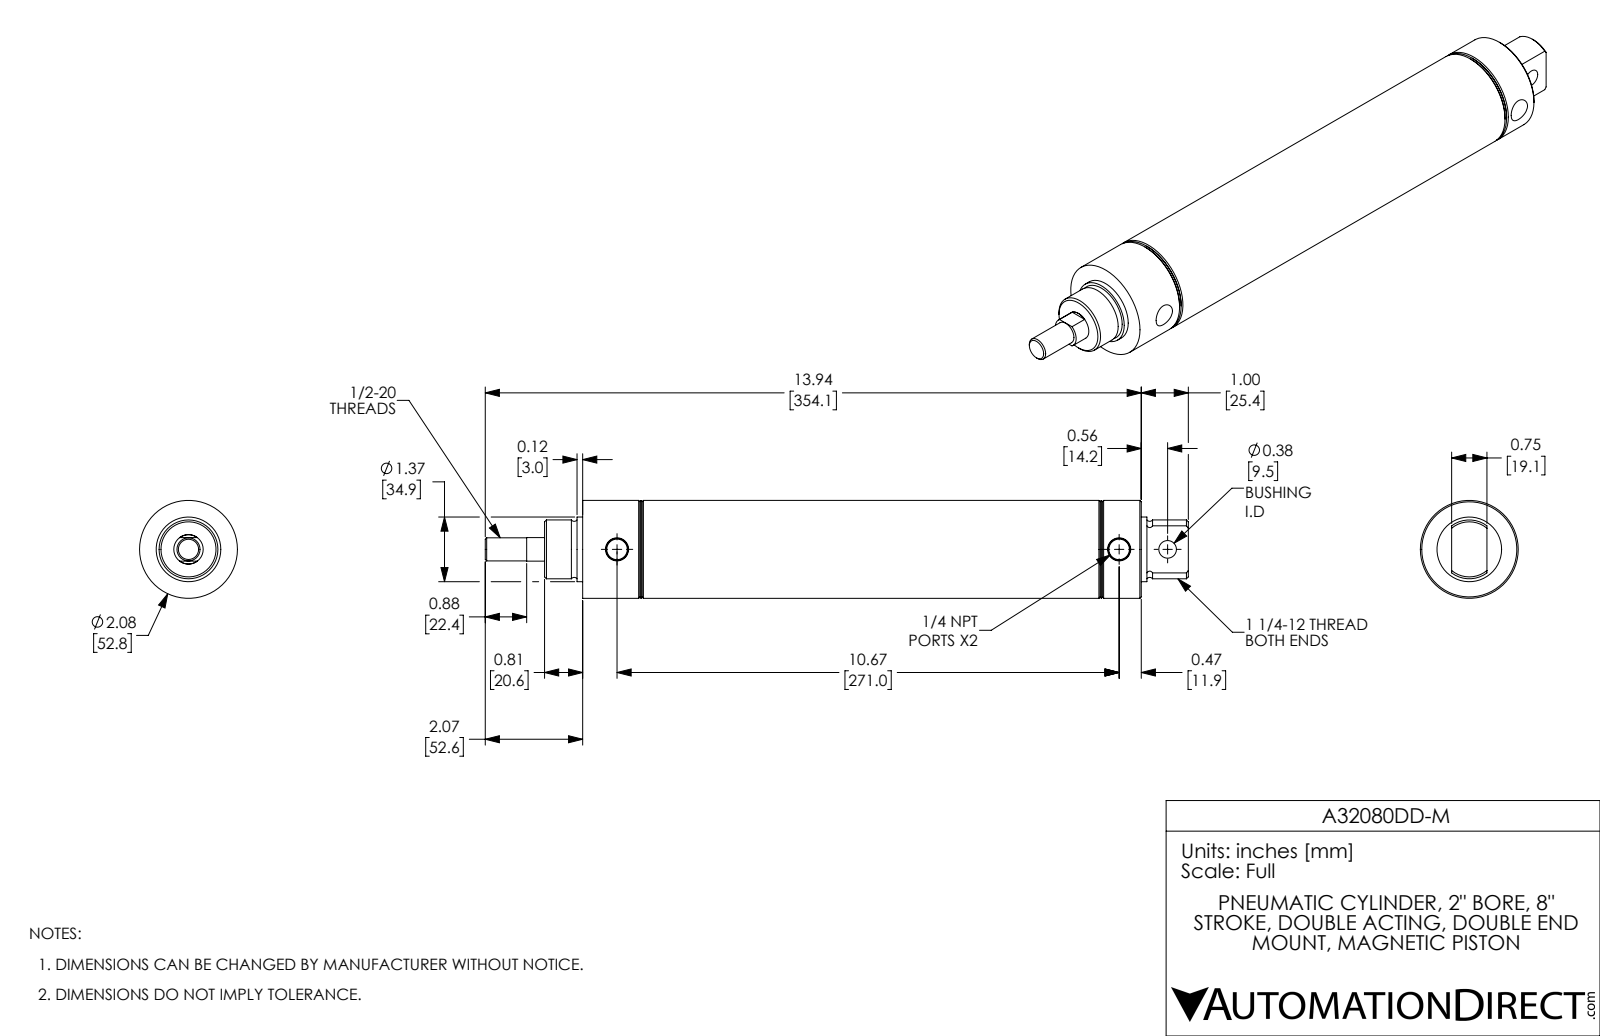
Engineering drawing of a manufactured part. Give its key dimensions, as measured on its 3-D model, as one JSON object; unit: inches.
{"part_name": "A32080DD-M; A32080DD-M-Rod; A32080DD-M-MainBody", "step_written_by": "SolidWorks 2017 (AUTOMOTIVE_DESIGN)", "units": "inches", "bodies": {"solids": 2, "faces": 88, "planar": 20, "cylindrical": 30, "other": 38}, "overall_size": [14.94, 2.08, 2.08], "volume_in3": 19.49, "surface_area_in2": 190.5, "round_holes": [[0.438, 2], [0.375, 1], [0.625, 1], [2, 1]], "round_bosses_or_shafts": [[2.08, 1], [1.373, 1], [1.25, 1], [0.491, 1]], "face_to_face_distances": [0.5, 8.5, 8, 10.185, 9.685, 1.685, 1.685, 2.185, 10.185, 11.87], "hole_center_spacings": [1.03, 10.67, 11.7]}
